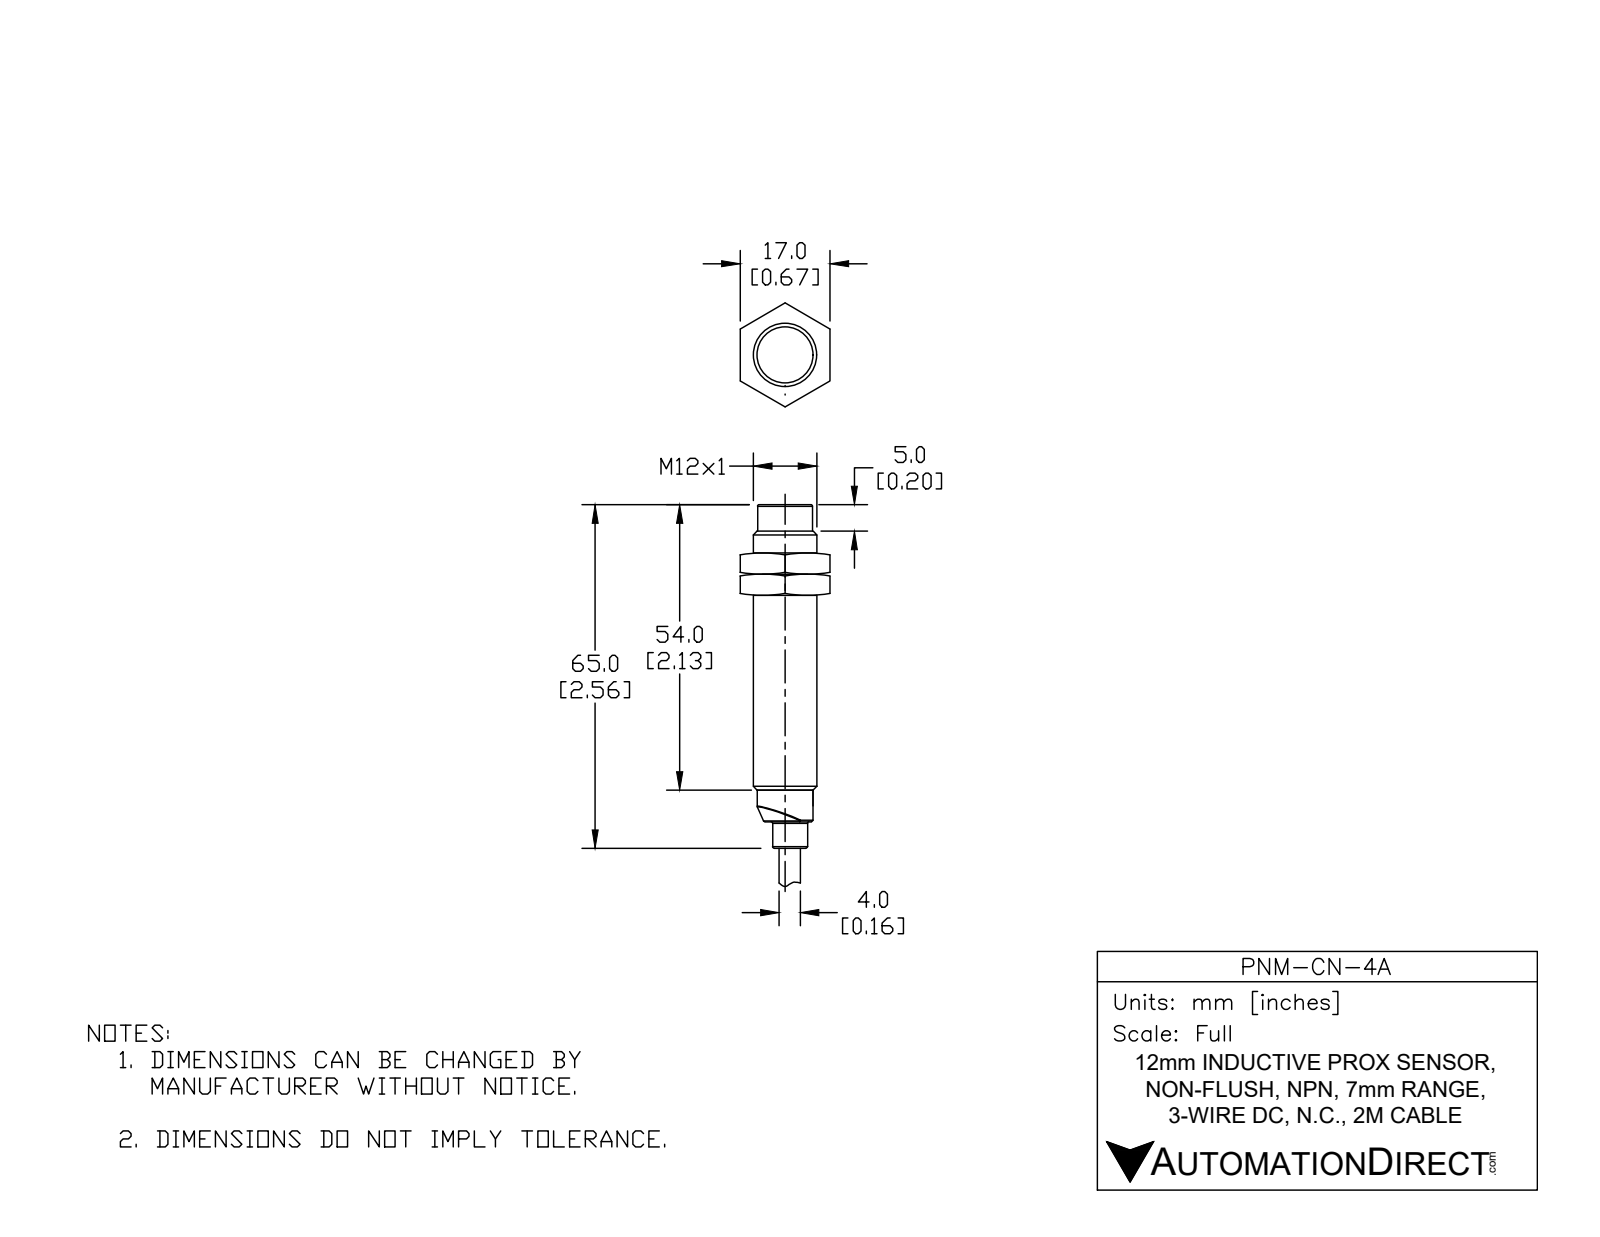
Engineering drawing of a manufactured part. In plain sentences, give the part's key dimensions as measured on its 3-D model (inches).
The part is named "PNM-CN-4A". Its 3-D file was written by "SolidWorks 2017 (AUTOMOTIVE_DESIGN)". It is 1 solid with 68 faces: 21 planar, 19 cylindrical and 28 other. Overall it measures 4.559 by 0.472 by 0.472 inches. Its volume is 0.452 cubic inches and its surface area 4.972 square inches. Round holes: 1 of diameter 0.161, 1 of diameter 0.401. Round bosses or shafts: 1 of diameter 0.472, 1 of diameter 0.417, 1 of diameter 0.415, 1 of diameter 0.384, 1 of diameter 0.26, 1 of diameter 0.157. Partial cylindrical surfaces (rounded edges, fillets, slot ends): 1 of radius 0.091. The main face-to-face distances are 2.362, 2.559, 0.197, 4.559, 2.197, 2, 0.022, 2.34, 2.537, 4.537. The hole center spacings are 0.039.
